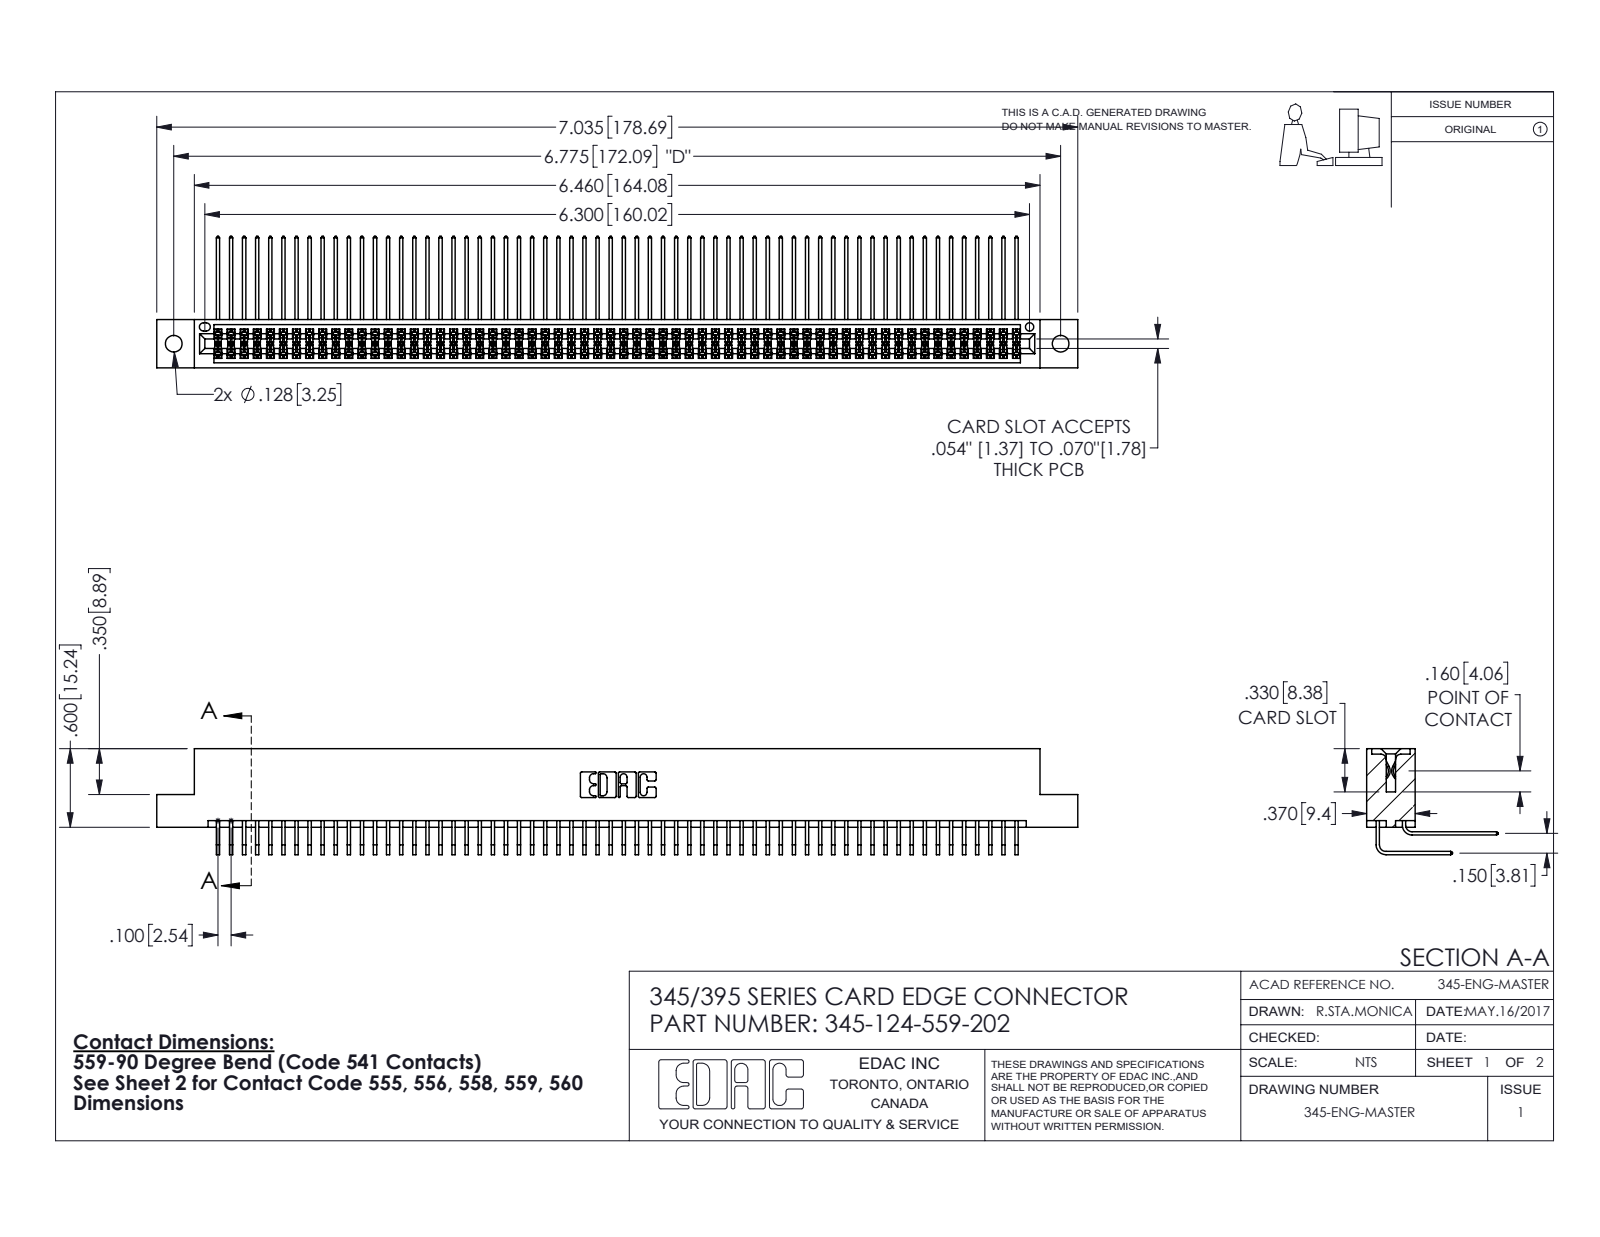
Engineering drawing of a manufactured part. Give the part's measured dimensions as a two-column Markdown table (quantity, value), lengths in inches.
| quantity | value |
| --- | --- |
| part name | 345-124-559-202; 345-292-001_559 Tail - 2; 345 Part_Flush Mounting Lugs - 0.128 Dia; 345-292-001_558 559 Tail - 1 |
| STEP written by | SolidWorks 2016 (CONFIG_CONTROL_DESIGN) |
| units | inches |
| bodies | 125 solids, 6574 faces (4420 planar, 2154 cylindrical, 0 other) |
| overall size | 7.035 × 1.005 × 0.809 |
| volume | 1.112 in³ |
| surface area | 47.14 in² |
| round holes (diameter × count) | 0.128 × 2, 0.064 × 1 |
| partial cylindrical surfaces (radius × count) | 0.006 × 248, 0.01 × 22, 0.007 × 6, 0.031 × 6, 0.026 × 3, 0.014 × 2, 0.019 × 2, 0.022 × 2 |
| main face-to-face distances | 0.072, 0.298, 0.2, 0.37, 0.098, 0.272, 0.025, 0.225, 0.175, 0.15 |
| hole center spacings | 0.27, 6.539, 6.775 |
